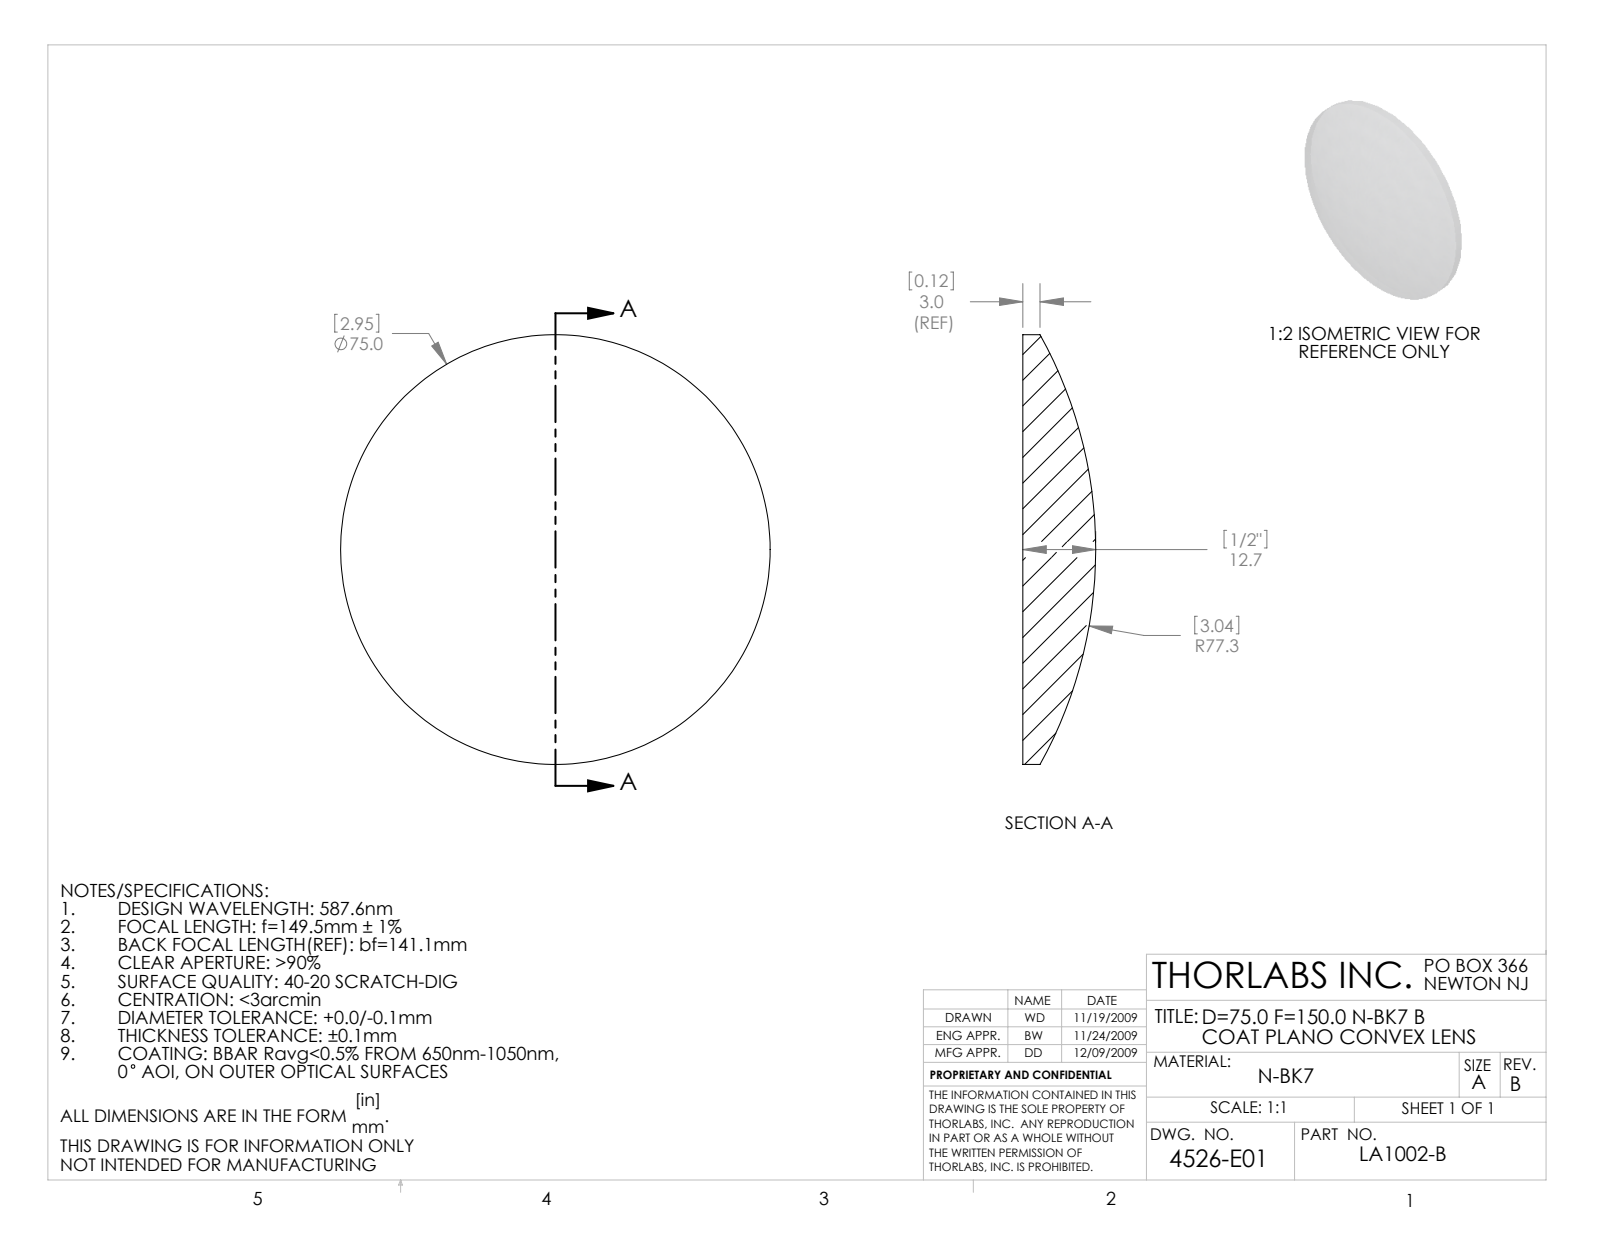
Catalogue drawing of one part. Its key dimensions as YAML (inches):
part_name: "4526-E0W"
step_written_by: "SolidWorks 2009 (AUTOMOTIVE_DESIGN)"
units: inches
bodies: {solids: 1, faces: 5, planar: 1, cylindrical: 2, other: 2}
overall_size: [2.953, 2.953, 0.5]
volume: 2.147
surface_area: 15.25
round_bosses_or_shafts:
  - {diameter: 2.953, count: 1}
